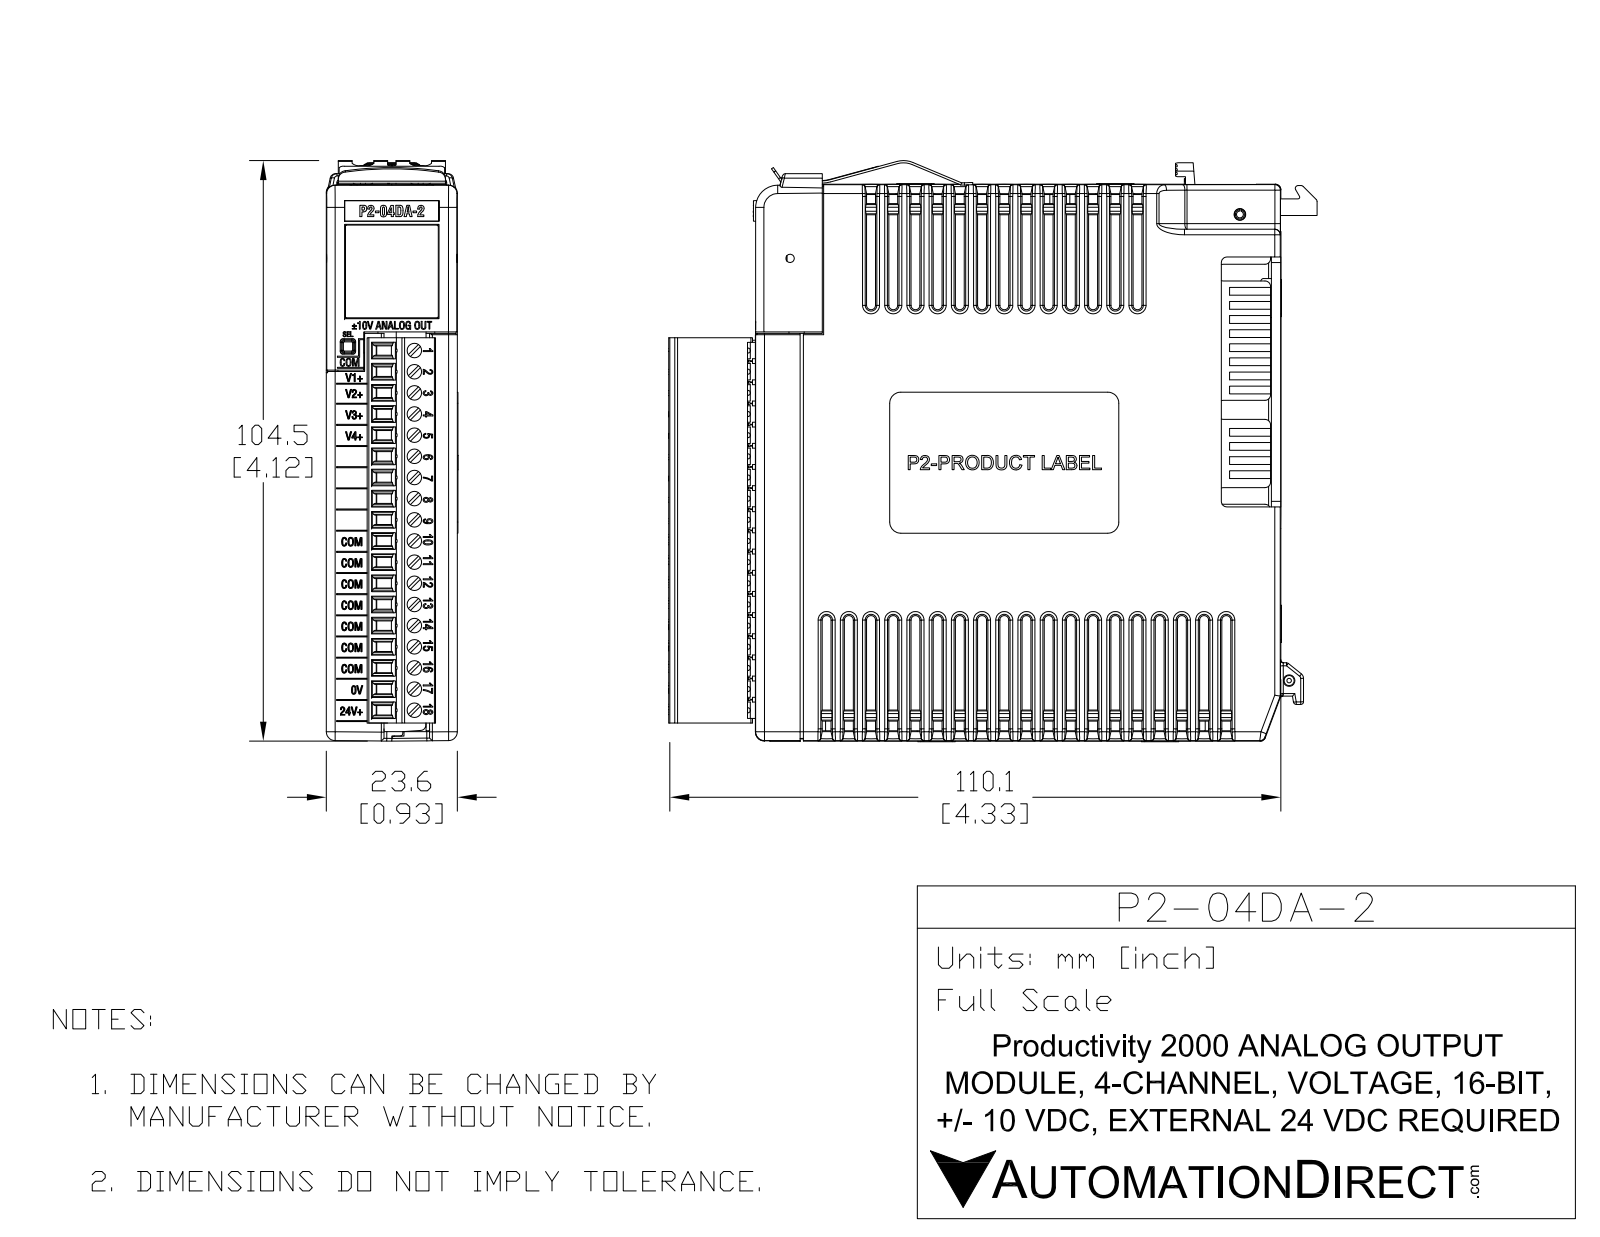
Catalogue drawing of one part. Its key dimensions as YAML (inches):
part_name: "P2-04DA-2 Red 2 Orig Coord 1 ext 1 comb 3 CC2 fXT fos wc1"
step_written_by: "SolidWorks 2017 (AUTOMOTIVE_DESIGN)"
units: inches
bodies: {solids: 2, faces: 4087, planar: 2722, cylindrical: 667, other: 698}
overall_size: [4.12, 4.106, 0.93]
volume: 11.22
surface_area: 77.25
round_holes:
  - {diameter: 0.049, count: 2}
  - {diameter: 0.059, count: 1}
  - {diameter: 0.079, count: 1}
  - {diameter: 0.083, count: 1}
  - {diameter: 0.098, count: 1}
partial_cylinders:
  - {radius: 0.02, count: 172}
  - {radius: 0.008, count: 128}
  - {radius: 0.039, count: 74}
  - {radius: 0.062, count: 34}
  - {radius: 0.059, count: 23}
  - {radius: 0.025, count: 20}
  - {radius: 0.063, count: 15}
  - {radius: 0.063, count: 13}
face_to_face_distances: [0.93, 0.063, 0.867, 0.75, 0.16, 0.77, 0.707, 0.804, 0.097, 0.222]
hole_center_spacings: [0.62, 3.206]
